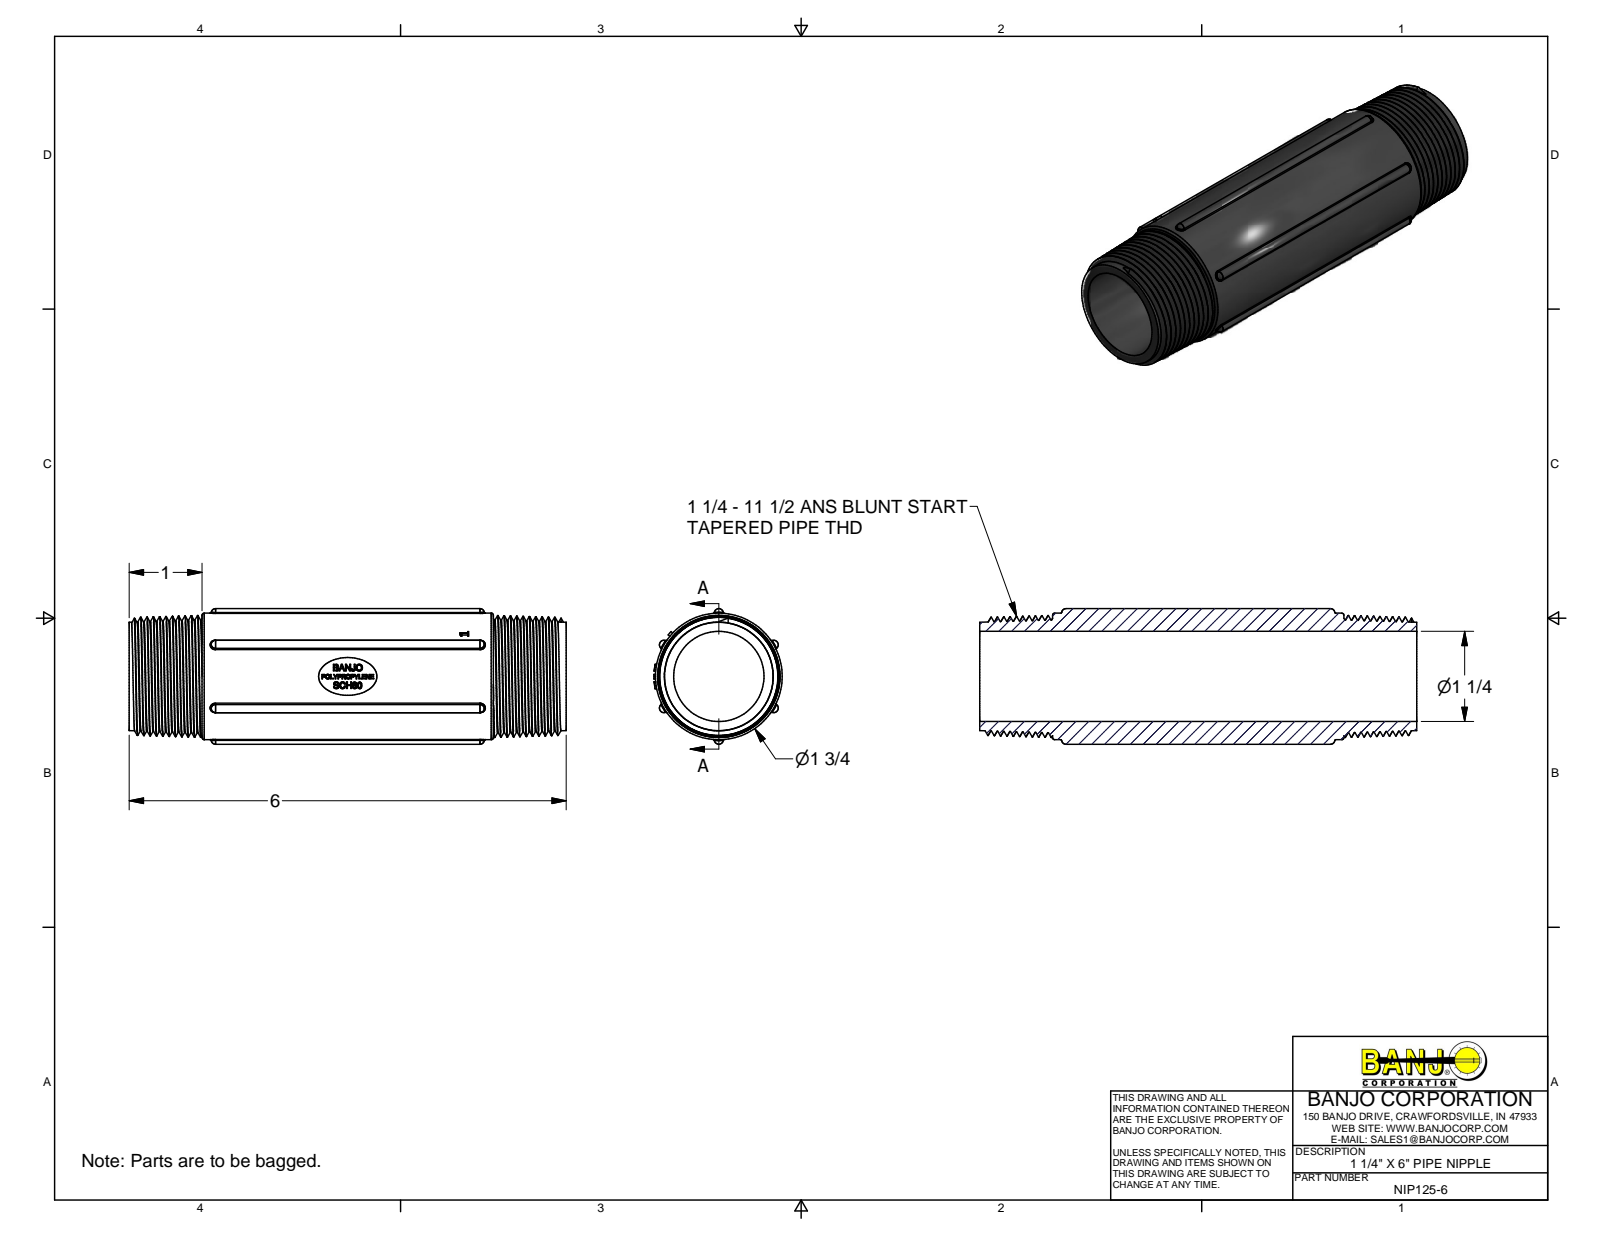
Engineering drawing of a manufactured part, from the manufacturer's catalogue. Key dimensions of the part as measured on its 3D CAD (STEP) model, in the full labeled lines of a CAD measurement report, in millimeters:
Part name (STEP PRODUCT): NIP125-6
STEP written by: Autodesk Inventor 2013 (AUTOMOTIVE_DESIGN)
Units: millimetres
Bodies: 1 solid, 423 faces (168 planar, 58 cylindrical, 197 other)
Overall size (bounding box): 152.4 × 47.4 × 44.7
Volume: 103 500 mm³ · Surface area: 42 770 mm²
Round holes (diameter × count): ⌀31.5 ×1
Round bosses / shafts (diameter × count): ⌀44.2 ×1
Partial cylindrical surfaces — rounded edges, fillets, slot ends (radius × count): R0.4 ×12, R1.6 ×6, R21.8 ×1, R22.6 ×1, R22.9 ×1
Main face-to-face distances: 152.4, 25.4, 127, 101.6, 1.5, 1.3, 1.2, 2.7, 1.6, 3
